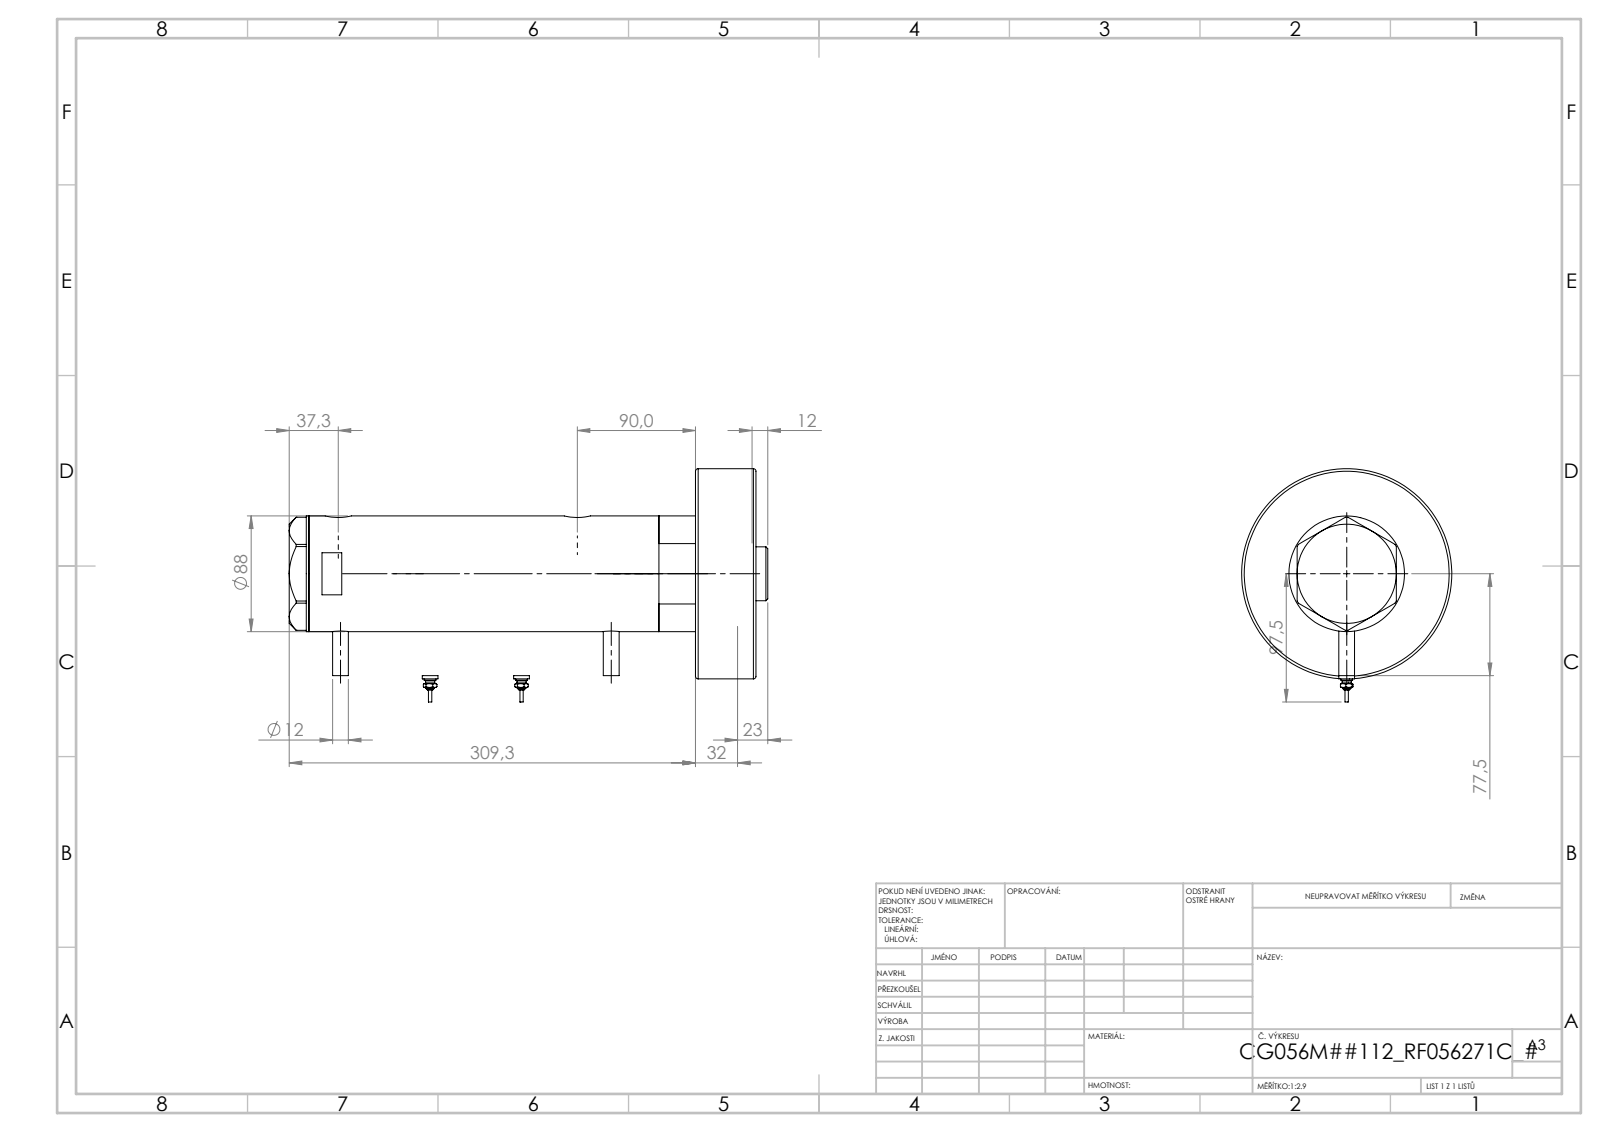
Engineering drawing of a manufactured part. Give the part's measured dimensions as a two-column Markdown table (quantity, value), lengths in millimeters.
| quantity | value |
| --- | --- |
| part name | V270CG_271C; V270CG_VC; V270CG_BACK; V270CG_SWITCH (+2 more) |
| STEP written by | SolidWorks 2019 (CONFIG_CONTROL_DESIGN) |
| units | millimeters |
| bodies | 7 solids, 242 faces (83 planar, 81 cylindrical, 78 other) |
| overall size | 336.47 × 160 × 160 |
| volume | 2 446 000 mm³ |
| surface area | 312 123 mm² |
| round holes (diameter × count) | 5 × 2, 12.5 × 2, 13.16 × 2, 20 × 2, 14.5 × 1, 42 × 1, 43.5 × 1, 56 × 1, 60 × 1, 75 × 1, 80 × 1 |
| round bosses / shafts (diameter × count) | 12 × 2, 9 × 2, 7 × 2, 4.34 × 2, 2.4 × 2, 160 × 1, 88 × 1, 73 × 1 |
| main face-to-face distances | 46, 263.9, 309.9, 186.4, 77.5, 123.5, 26, 160.4, 237.9, 283.9 |
| hole center spacings | 1.7, 25.8, 162.3, 164, 188.1, 189.8 |
